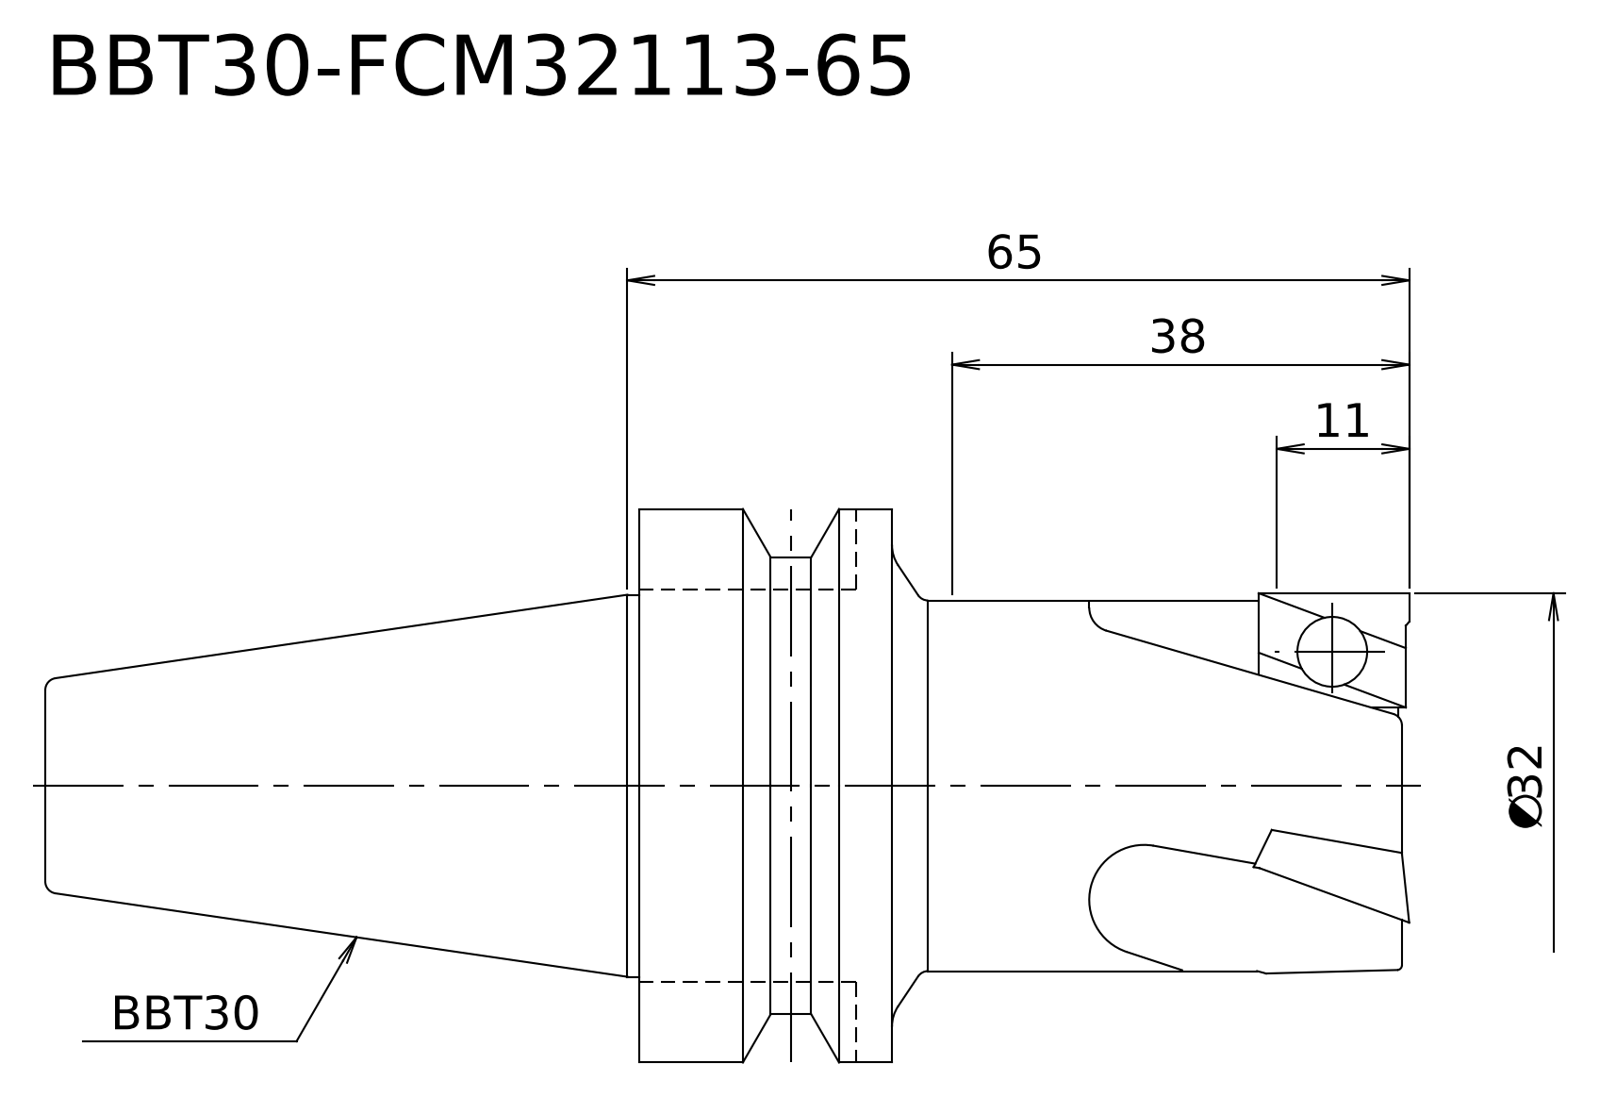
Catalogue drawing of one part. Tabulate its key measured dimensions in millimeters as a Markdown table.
| quantity | value |
| --- | --- |
| STEP written by | Kubotek KeyCreator V8.5.1 (14335) (CONFIG_CONTROL_DESIGN) |
| units | millimeters |
| bodies | 1 solid, 17 faces (4 planar, 6 cylindrical, 7 other) |
| overall size | 113.4 × 46 × 46 |
| volume | 89 708 mm³ |
| surface area | 14 268 mm² |
| round bosses / shafts (diameter × count) | 46 × 1, 38 × 1, 32 × 1, 31.75 × 1, 30.8 × 1 |
| main face-to-face distances | 64, 43, 21, 113.4, 70.4, 49.4 |
